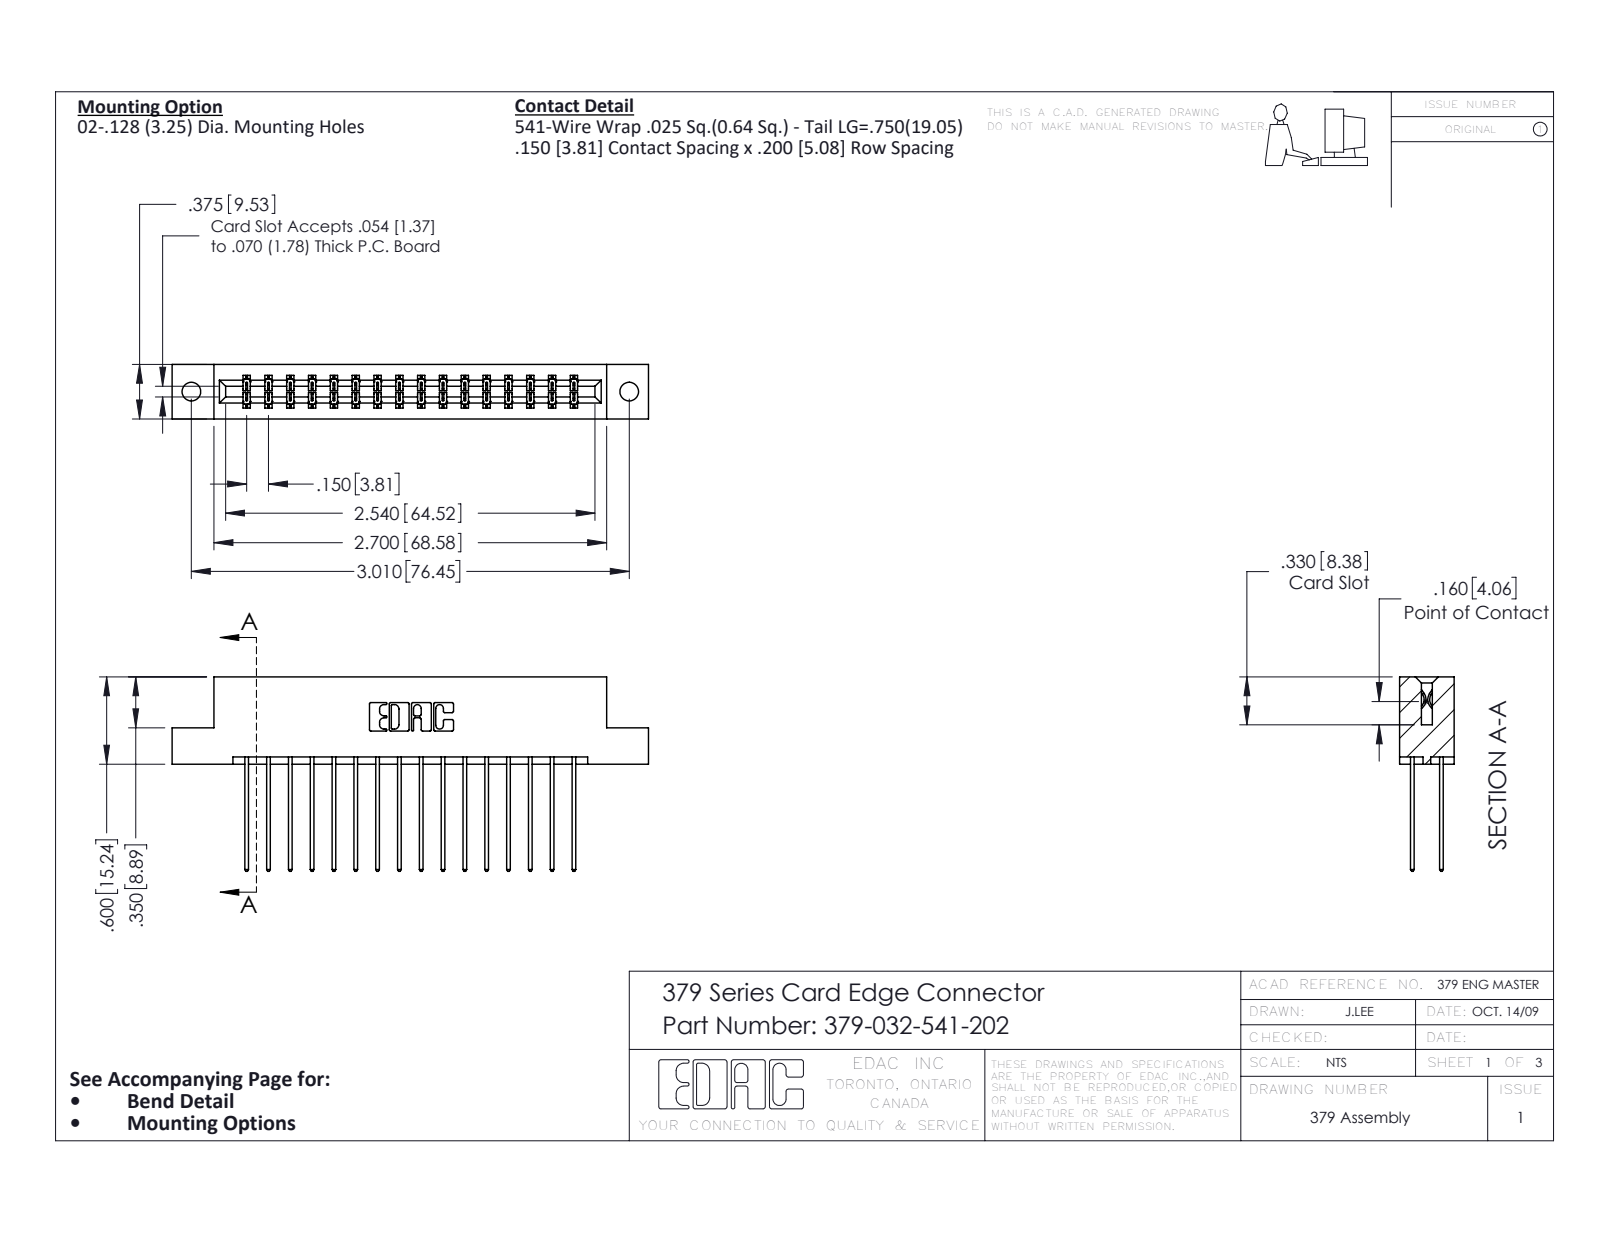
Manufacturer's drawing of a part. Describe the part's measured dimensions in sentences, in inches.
The part is named "345-292-001_345-293-141; 379-032-541-202; 379 Part_Flush - .128 Dia". Its 3-D file was written by "SolidWorks 2020 (CONFIG_CONTROL_DESIGN)". It is 33 solids with 1778 faces: 1222 planar, 556 cylindrical and 0 other. Overall it measures 3.275 by 1.337 by 0.375 inches. Its volume is 0.53 cubic inches and its surface area 15.75 square inches. Round holes: 2 of diameter 0.128. Partial cylindrical surfaces (rounded edges, fillets, slot ends): 48 of radius 0.006, 32 of radius 0.01, 22 of radius 0.01, 6 of radius 0.007, 6 of radius 0.031, 3 of radius 0.026, 2 of radius 0.014, 2 of radius 0.022. The main face-to-face distances are 0.3, 0.075, 0.2, 0.1, 0.375, 0.275, 0.15, 0.025, 0.05, 0.6. The hole center spacings are 3.01.
